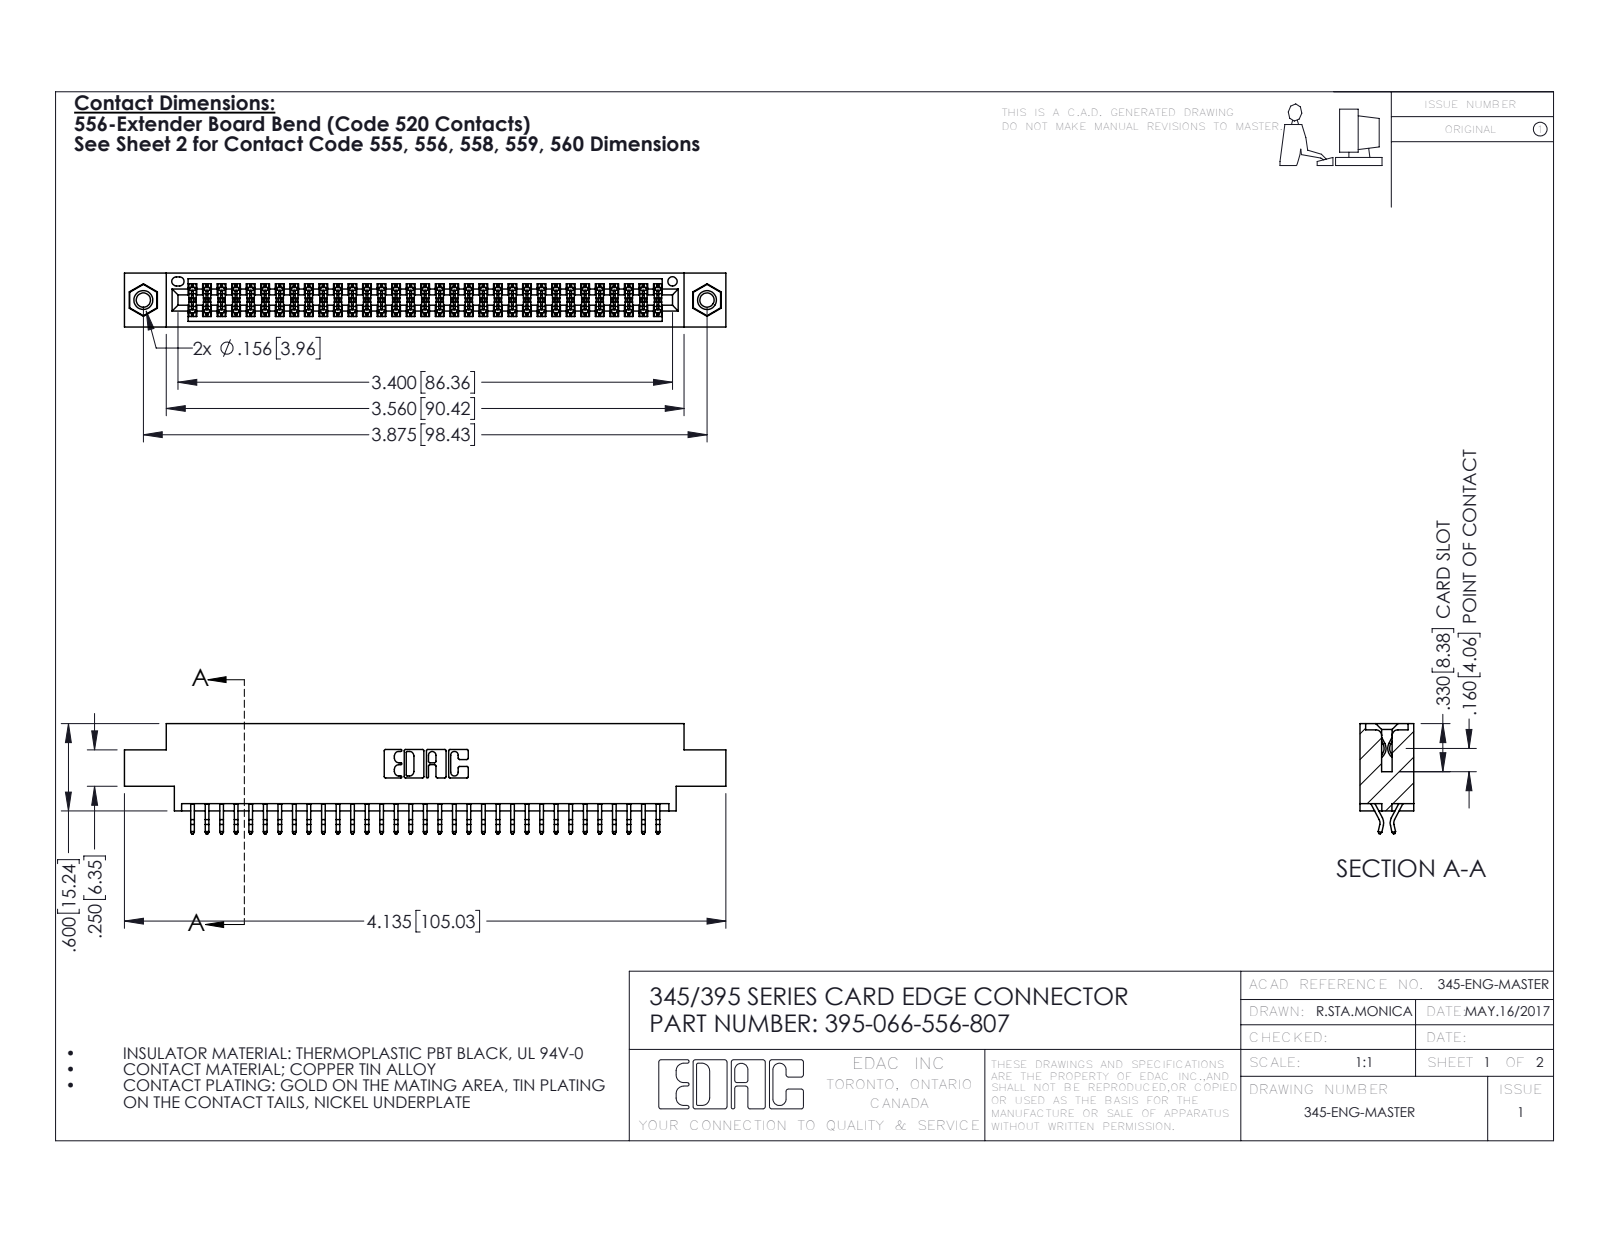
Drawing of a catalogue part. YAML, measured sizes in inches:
part_name: "345 Part_0.170 Offset - 0.156 Dia-TI; 345-250-001_345-250-005-103; 345-292-001_556 Tail; 395-066-556-807"
step_written_by: "SolidWorks 2016 (CONFIG_CONTROL_DESIGN)"
units: inches
bodies: {solids: 69, faces: 3886, planar: 2558, cylindrical: 1312, other: 16}
overall_size: [4.135, 0.757, 0.37]
volume: 0.61
surface_area: 22.79
round_holes:
  - {diameter: 0.098, count: 2}
  - {diameter: 0.125, count: 2}
  - {diameter: 0.156, count: 2}
  - {diameter: 0.064, count: 1}
round_bosses_or_shafts:
  - {diameter: 0.155, count: 2}
partial_cylinders:
  - {radius: 0.006, count: 99}
  - {radius: 0.01, count: 22}
  - {radius: 0.007, count: 6}
  - {radius: 0.031, count: 6}
  - {radius: 0.026, count: 3}
  - {radius: 0.01, count: 2}
  - {radius: 0.014, count: 2}
  - {radius: 0.019, count: 2}
face_to_face_distances: [0.072, 0.298, 0.37, 0.2, 0.025, 0.098, 0.272, 0.225, 0.175, 0.149]
hole_center_spacings: [0.27, 3.64, 3.875]
